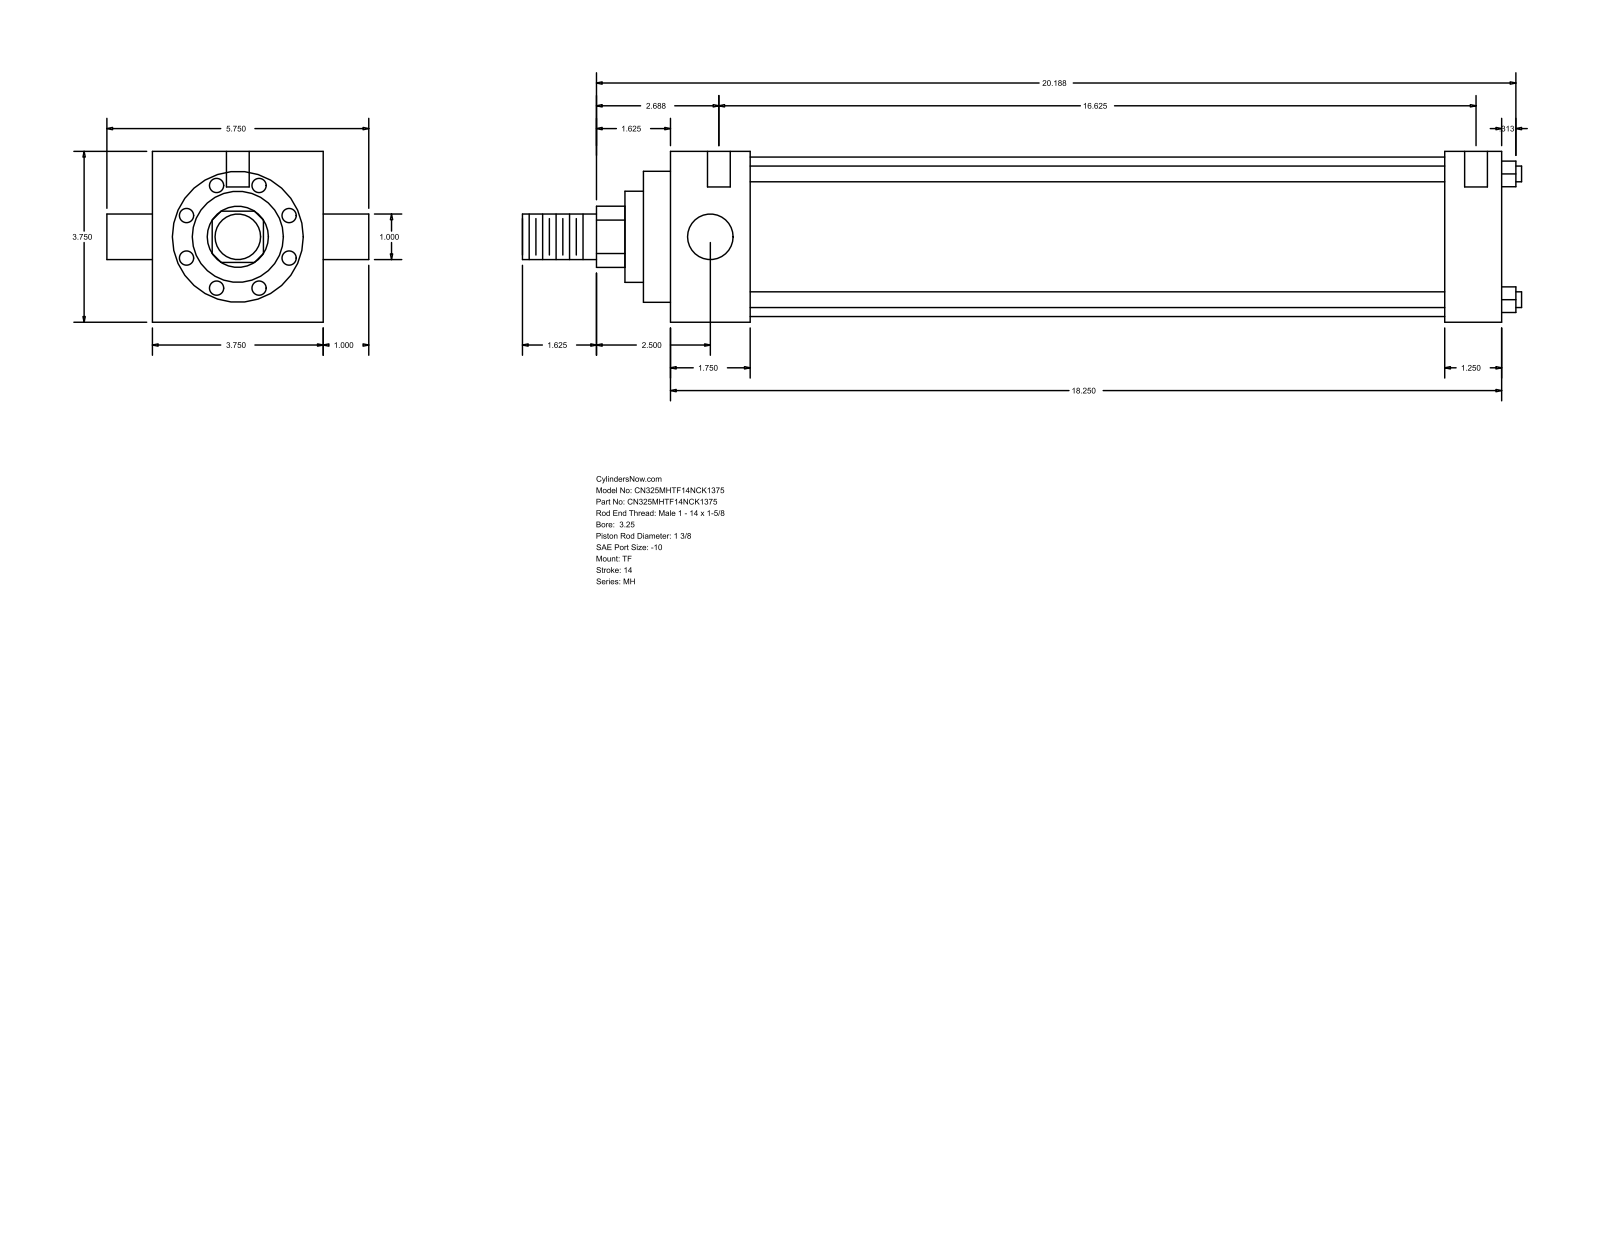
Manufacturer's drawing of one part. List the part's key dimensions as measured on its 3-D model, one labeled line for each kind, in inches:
Part name (STEP PRODUCT): MH_TF__0325_1.375
STEP written by: GSSL Pune (CONFIG_CONTROL_DESIGN)
Units: inches
Bodies: 0 solids, 86 faces (61 planar, 25 cylindrical, 0 other)
Overall size (bounding box): 21.937 × 5.75 × 3.75
Round holes (diameter × count): ⌀0.219 ×3, ⌀0.5 ×2
Round bosses / shafts (diameter × count): ⌀0.345 ×4, ⌀1 ×2, ⌀3.5 ×1, ⌀2.875 ×1, ⌀2 ×1, ⌀1.375 ×1
Partial cylindrical surfaces — rounded edges, fillets, slot ends (radius × count): R0.672 ×1
Main face-to-face distances: 3.75, 18.25, 1.75, 17, 15.25, 16.5, 1.25, 0.594, 2.344, 17.594
Hole centre spacings: 0.063, 0.187, 16.625, 16.688, 16.813, 16.875
